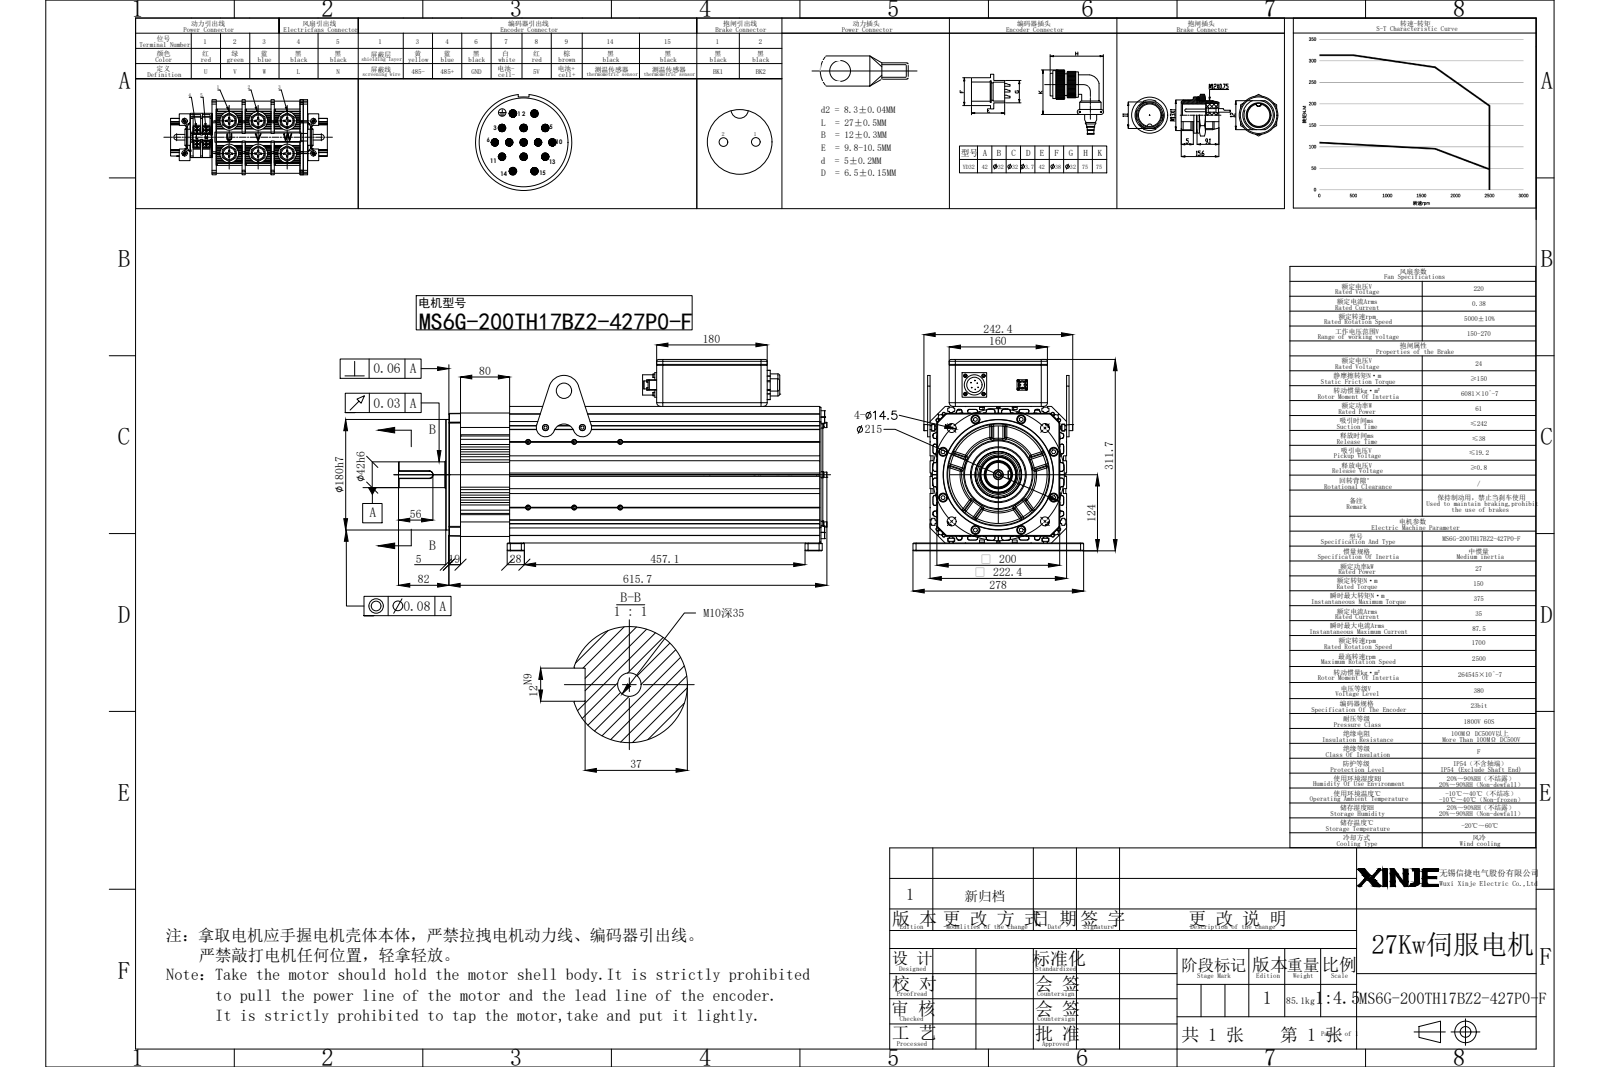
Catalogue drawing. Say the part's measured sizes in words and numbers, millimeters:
The part is named "MS6G-200TH17BZ2-427P0". Its 3-D file was written by "SolidWorks 2022 (CONFIG_CONTROL_DESIGN)". It is 105 solids with 6081 faces: 4113 planar, 1010 cylindrical and 958 other. Overall it measures 697.7 by 311.7 by 278 millimeters. Its volume is 29 800 000 cubic millimeters and its surface area 3 333 000 square millimeters. Round holes: 22 of diameter 5, 18 of diameter 3.3, 18 of diameter 8, 12 of diameter 14.5, 11 of diameter 6.8, 10 of diameter 13, 8 of diameter 7.5, 8 of diameter 10, 4 of diameter 2.5, 4 of diameter 4, 4 of diameter 4.67, 4 of diameter 6.2. Round bosses or shafts: 19 of diameter 4, 18 of diameter 10, 18 of diameter 7, 18 of diameter 6, 12 of diameter 3, 9 of diameter 13, 8 of diameter 8, 6 of diameter 1. Partial cylindrical surfaces (rounded edges, fillets, slot ends): 24 of radius 3, 20 of radius 2, 16 of radius 0.5, 13 of radius 1, 8 of radius 1.25, 8 of radius 5.76, 8 of radius 10, 5 of radius 6. The main face-to-face distances are 222.4, 0.71, 17.11, 205.29, 16.86, 205.54, 3, 10.7, 211.7, 13.7. The hole center spacings are 75, 150, 38.4, 41.18, 61.7, 76.17, 97.5, 99.3.
